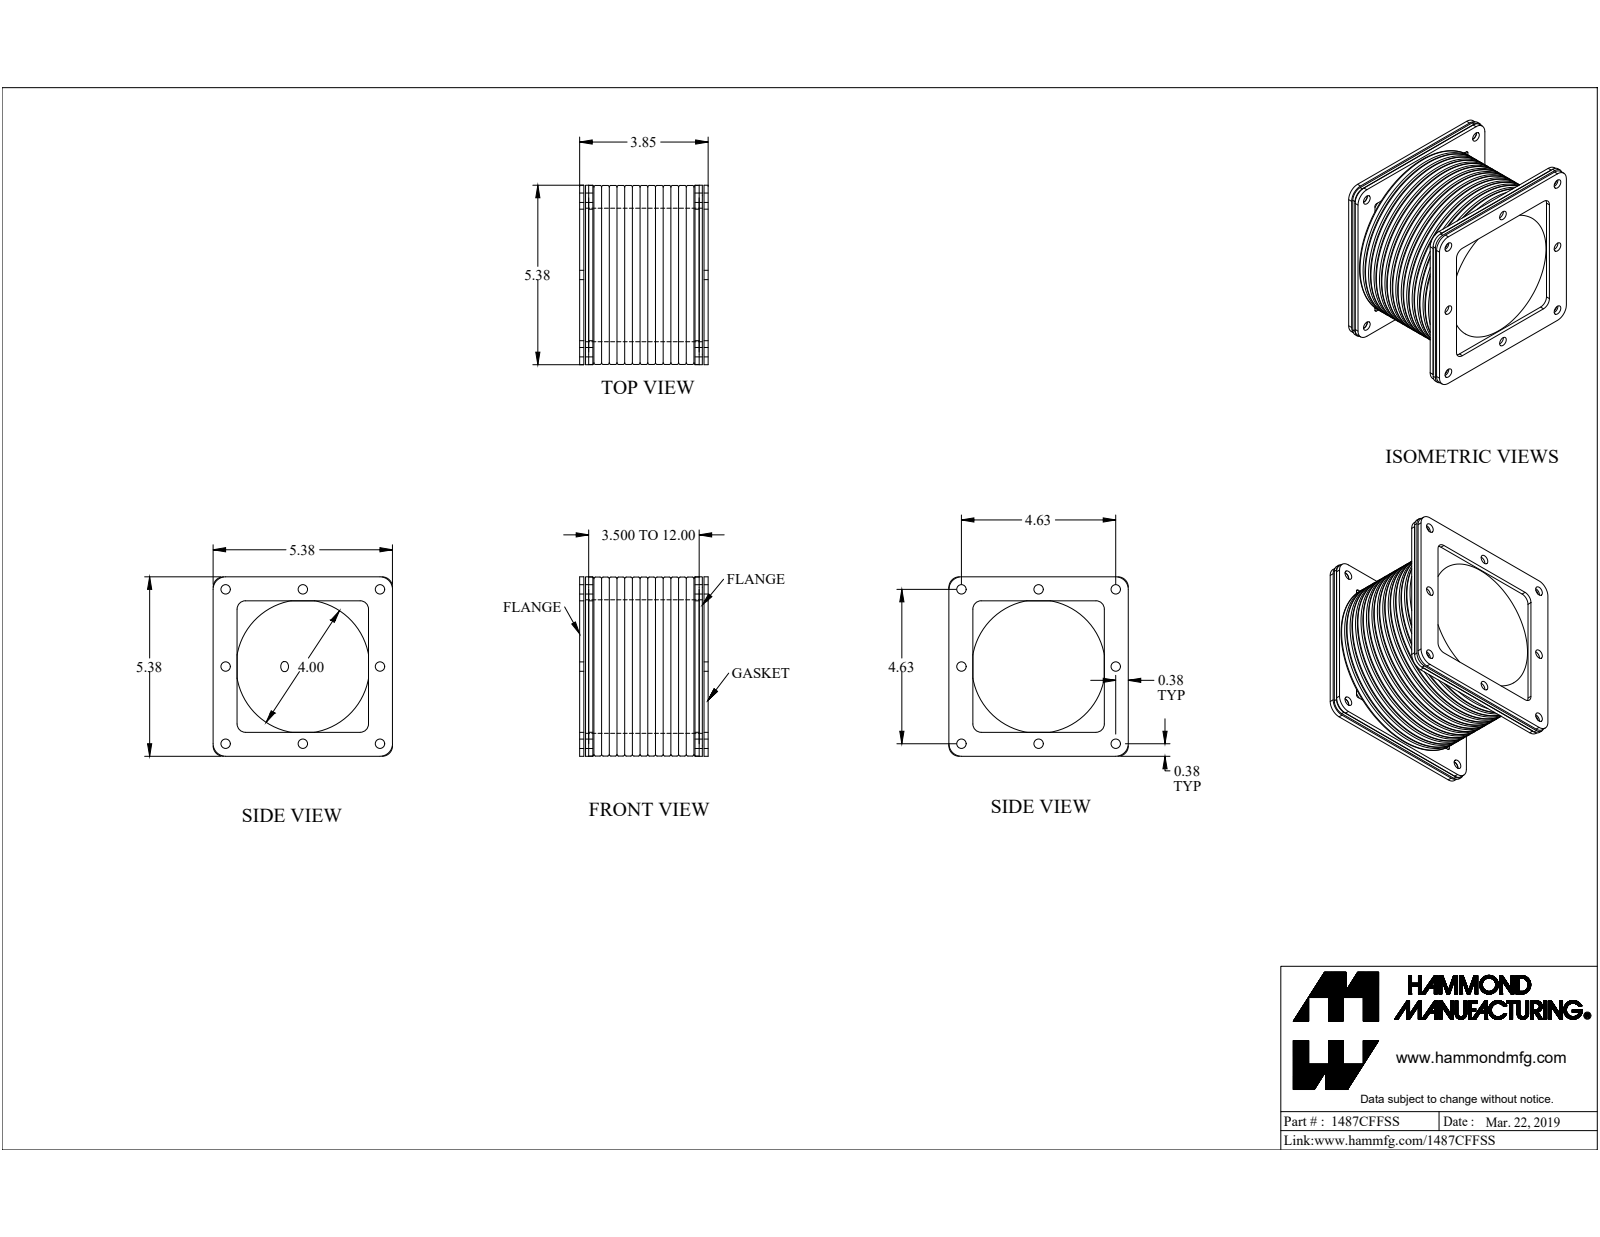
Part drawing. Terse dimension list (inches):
name: 1487CFFSS
written by: SolidWorks 2019 (CONFIG_CONTROL_DESIGN)
unit: in
bodies: 11 solids, 342 faces (166 planar, 132 cylindrical, 44 other)
size: 5.375 × 5.375 × 4.501
volume: 42.55 in³; area: 290.3 in²
holes: 8× ⌀0.281, 4× ⌀0.281, 1× ⌀0.196, 1× ⌀0.258, 1× ⌀0.35, 1× ⌀4
bosses: 1× ⌀5.362, 1× ⌀0.5, 1× ⌀0.25
rounds: 12× R0.02, 4× R0.062, 4× R0.25, 4× R0.313, 4× R0.375
face distances: 0.125, 0.27, 3.455, 0.095, 3.405, 0.22, 3.28, 3.185, 0.05, 0.145
hole spacings: 2.313, 3.27, 5.171, 4.625, 6.541
